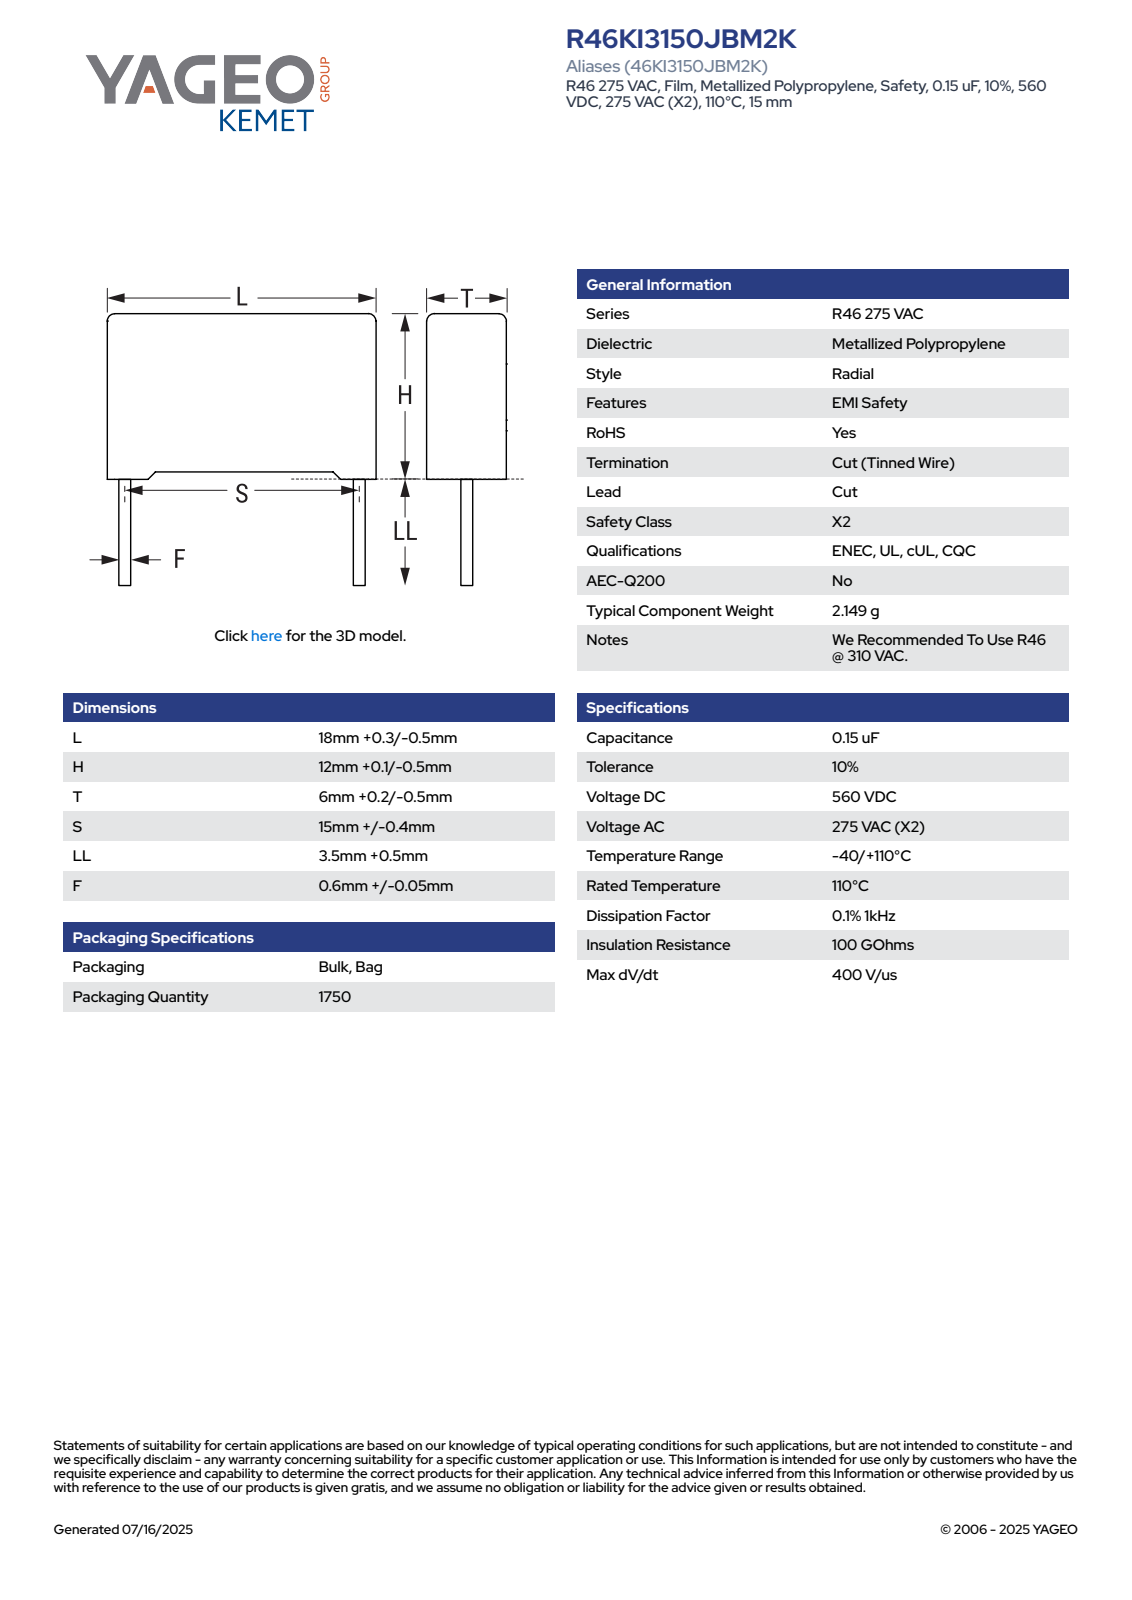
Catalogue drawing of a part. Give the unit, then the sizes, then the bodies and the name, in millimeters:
Units: millimetres
Overall size (bounding box): 18.3 × 16.1 × 6.21
Round bosses / shafts (diameter × count): ⌀0.65 ×2
Partial cylindrical surfaces — rounded edges, fillets, slot ends (radius × count): R0.5 ×4
Main face-to-face distances: 6.2, 11.35, 18.3, 0.61, 5.59, 0.75, 12.1, 0.42, 0.33, 11.68
Volume: 1 304 mm³ · Surface area: 868 mm²
Bodies: 4 solids, 85 faces (77 planar, 8 cylindrical, 0 other)
Part name (STEP PRODUCT): CFR_RB2_18X12X6_L18.3H12.1T6.2S15LL4F0.65
STEP written by: SolidWorks 2021 (AUTOMOTIVE_DESIGN)
